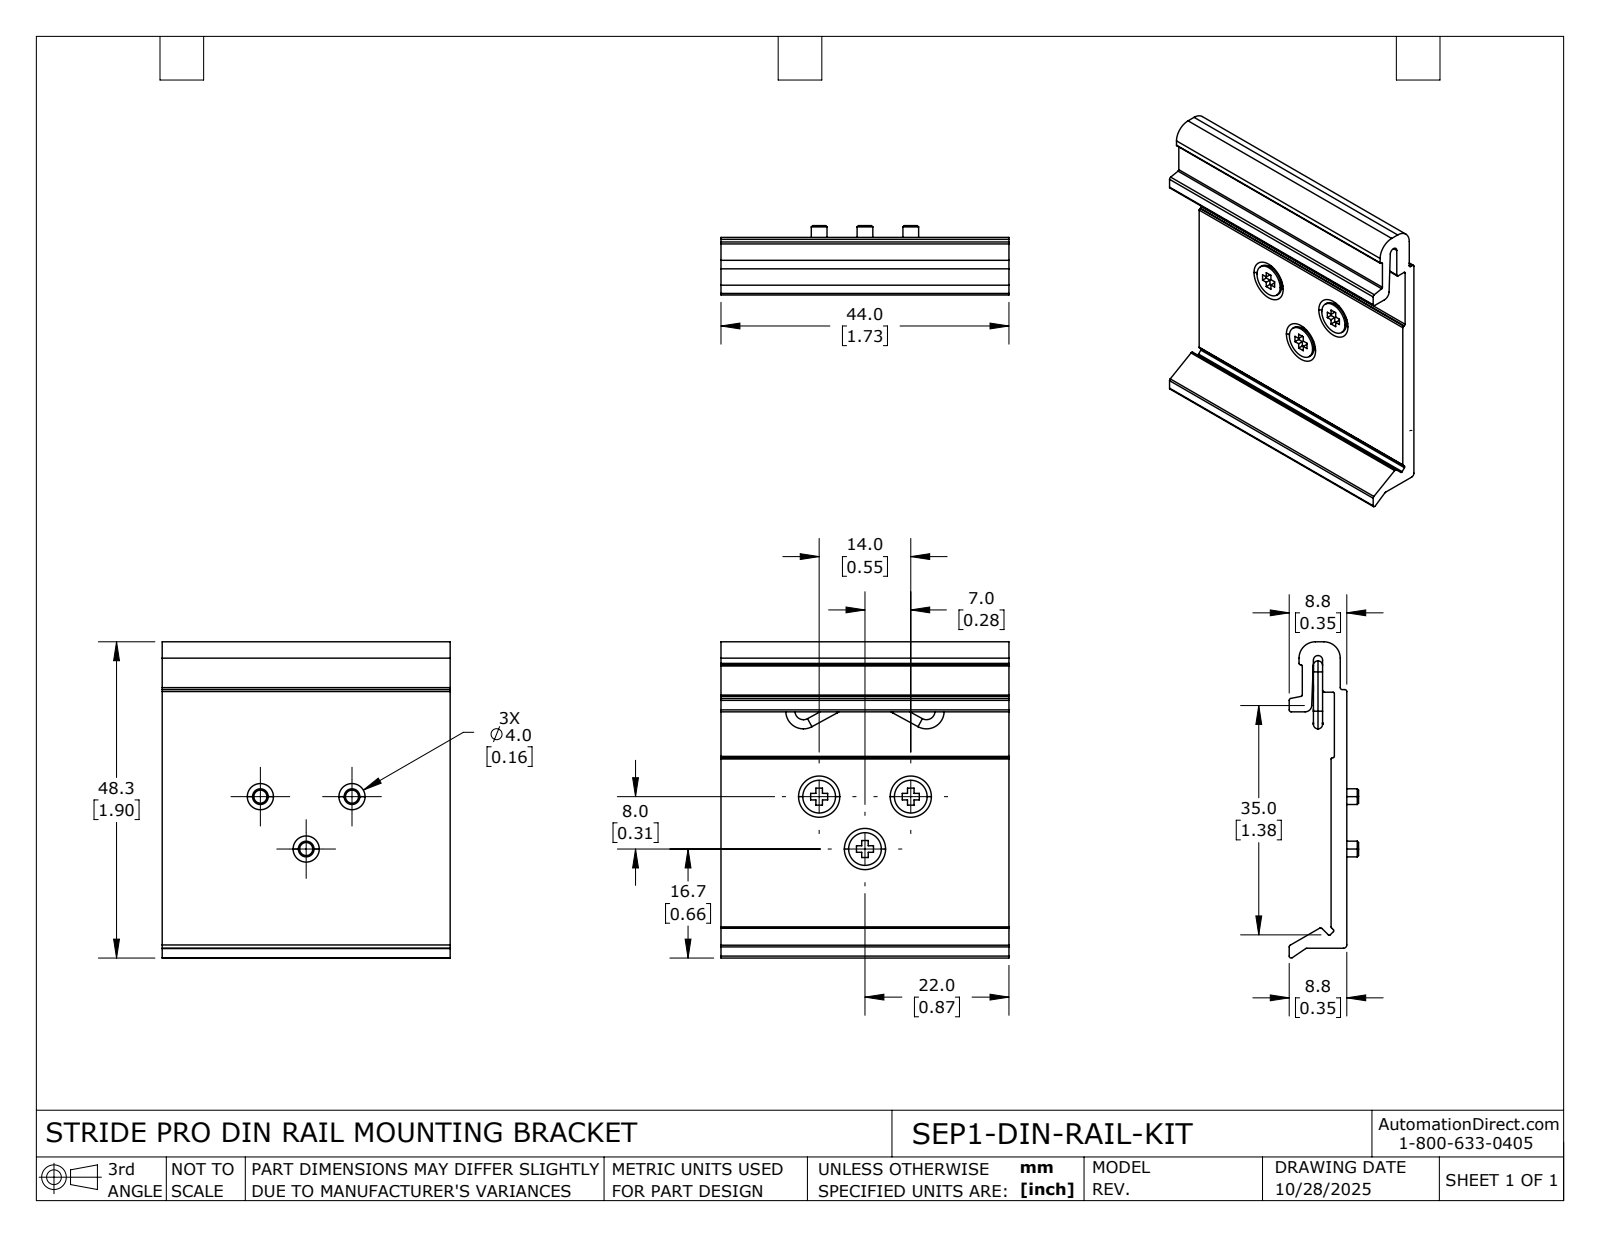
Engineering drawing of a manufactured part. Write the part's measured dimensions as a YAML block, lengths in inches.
part_name: "SEP1-DIN-RAIL-KIT"
step_written_by: "SolidWorks 2024 (AUTOMOTIVE_DESIGN)"
units: inches
bodies: {solids: 5, faces: 238, planar: 138, cylindrical: 75, other: 25}
overall_size: [2.756, 1.732, 0.402]
volume: 0.32
surface_area: 15.65
round_holes:
  - {diameter: 0.157, count: 8}
  - {diameter: 0.118, count: 2}
round_bosses_or_shafts:
  - {diameter: 0.315, count: 2}
  - {diameter: 0.244, count: 2}
  - {diameter: 0.205, count: 2}
partial_cylinders:
  - {radius: 0.039, count: 10}
  - {radius: 0.047, count: 10}
  - {radius: 0.079, count: 4}
  - {radius: 0.104, count: 4}
  - {radius: 0.024, count: 2}
  - {radius: 0.02, count: 1}
  - {radius: 0.059, count: 1}
  - {radius: 0.118, count: 1}
face_to_face_distances: [0.047, 0.039, 0.339, 1.685, 0.299, 0.252, 0.291, 1.638, 1.732, 0.098]
hole_center_spacings: [0.419, 0.533, 0.616, 0.668, 0.998, 1.02, 1.263, 1.393]
